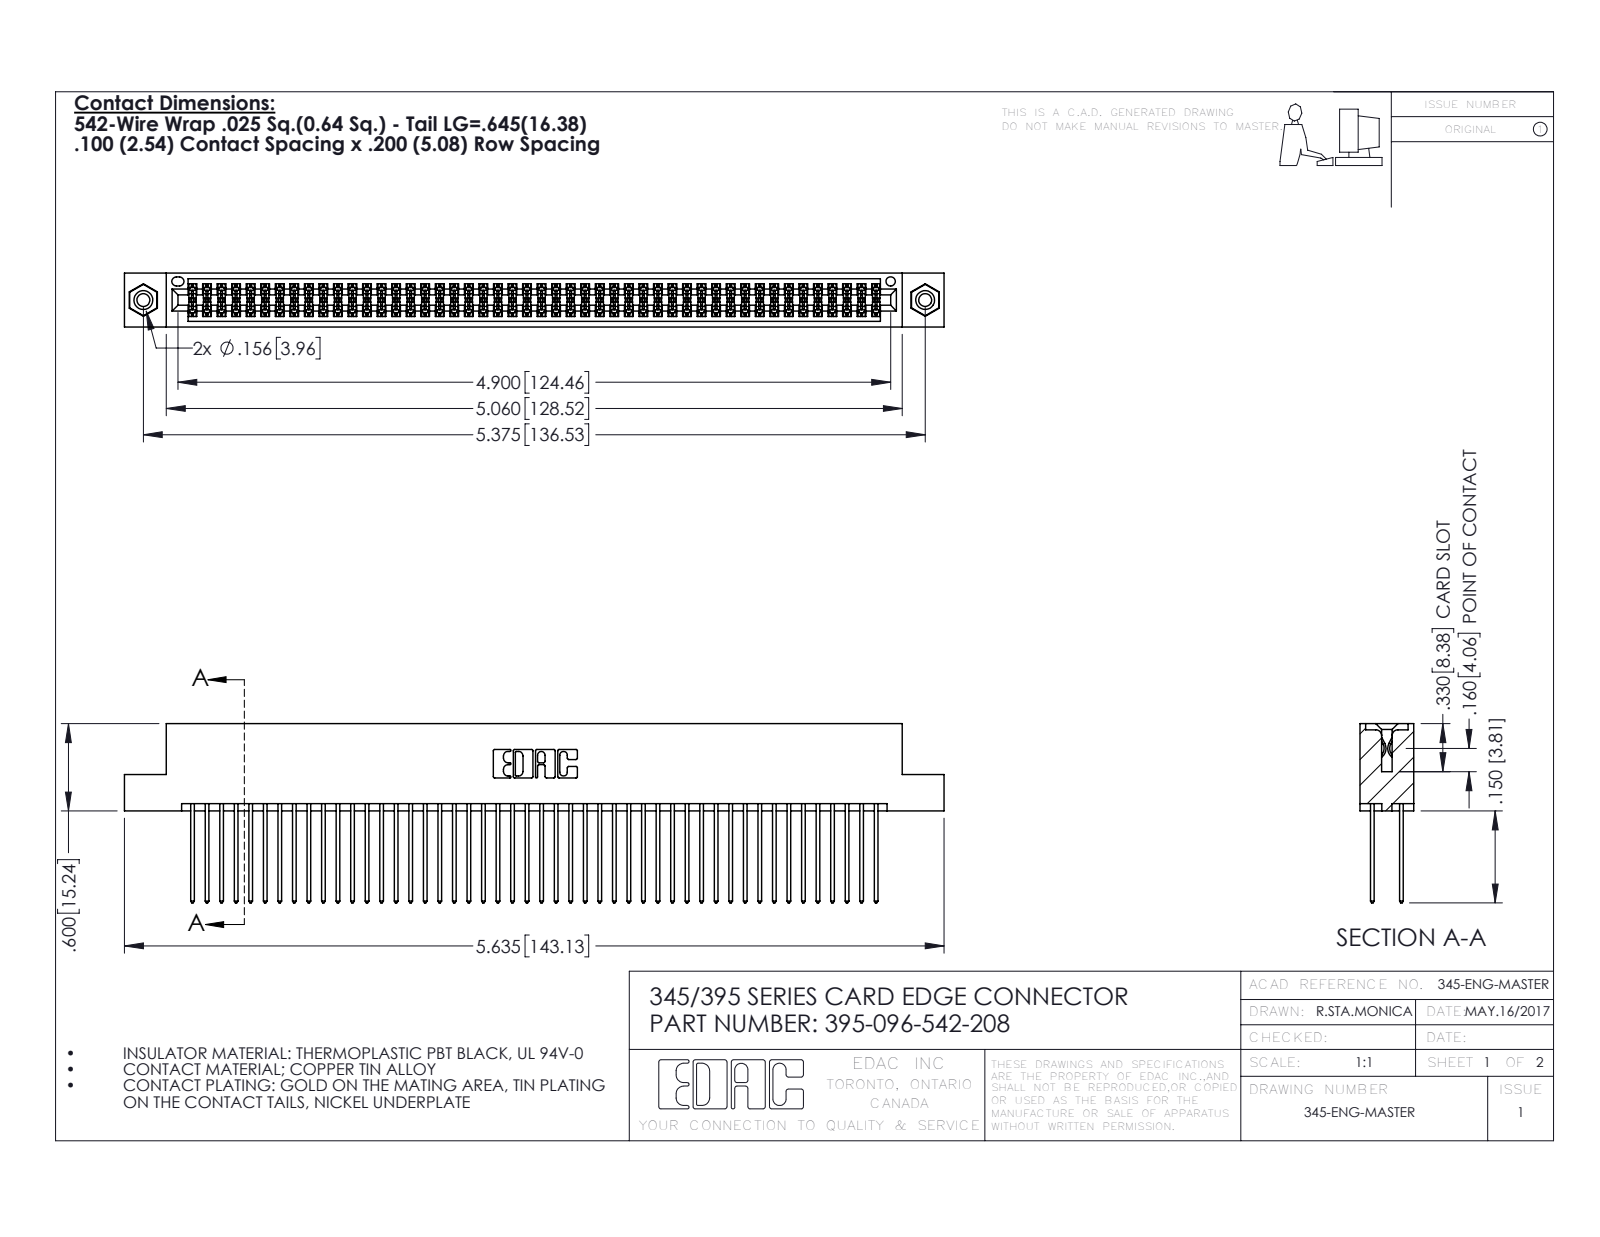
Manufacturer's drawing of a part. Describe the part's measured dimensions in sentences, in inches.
The part is named "395-096-542-208; 345-250-001_345-250-003-102; 345 Part_Flush Mounting Lugs - 0.156 Dia-TI; 345-292-001_345-293-142". Its 3-D file was written by "SolidWorks 2016 (CONFIG_CONTROL_DESIGN)". It is 99 solids with 4986 faces: 3280 planar, 1690 cylindrical and 16 other. Overall it measures 5.635 by 1.232 by 0.37 inches. Its volume is 0.879 cubic inches and its surface area 36.44 square inches. Round holes: 2 of diameter 0.089, 2 of diameter 0.125, 2 of diameter 0.156, 1 of diameter 0.064. Round bosses or shafts: 2 of diameter 0.155. Partial cylindrical surfaces (rounded edges, fillets, slot ends): 144 of radius 0.006, 96 of radius 0.01, 22 of radius 0.01, 6 of radius 0.007, 6 of radius 0.031, 3 of radius 0.026, 2 of radius 0.014, 2 of radius 0.019. The main face-to-face distances are 0.072, 0.298, 0.2, 0.098, 0.272, 0.025, 0.225, 0.37, 0.175, 0.149. The hole center spacings are 0.27, 5.139, 5.375.
